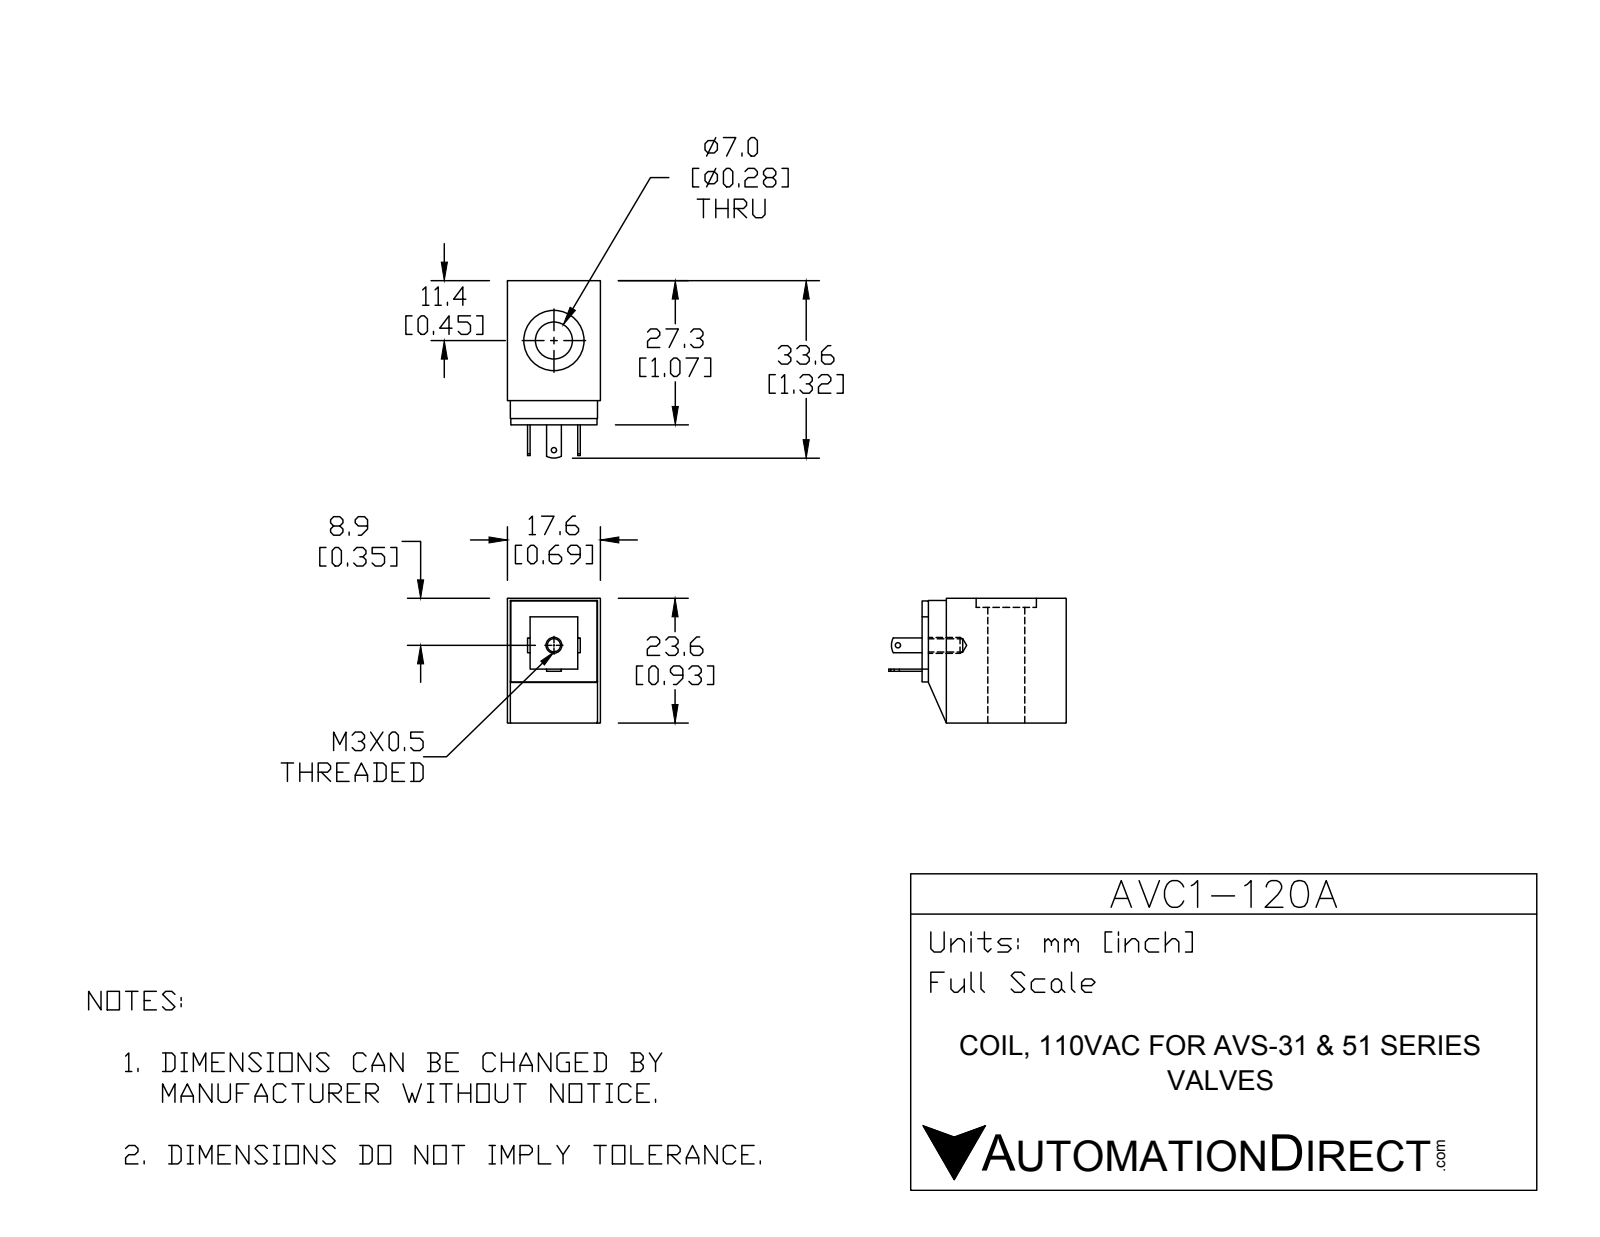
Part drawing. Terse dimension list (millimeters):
name: AVC1-120A
written by: SolidWorks 2016 (AUTOMOTIVE_DESIGN)
unit: mm
bodies: 1 solid, 69 faces (31 planar, 32 cylindrical, 6 other)
size: 33.6 × 23.6 × 17.6
volume: 9 679 mm³; area: 3 645 mm²
holes: 2× ⌀1, 1× ⌀2.5, 1× ⌀7, 1× ⌀11.4
rounds: 16× R0.1, 2× R3
face distances: 17.6, 23.6, 27.3, 0.55, 17.05, 1.2, 26.1, 13.3, 0.4, 16.5
hole spacings: 20.75
